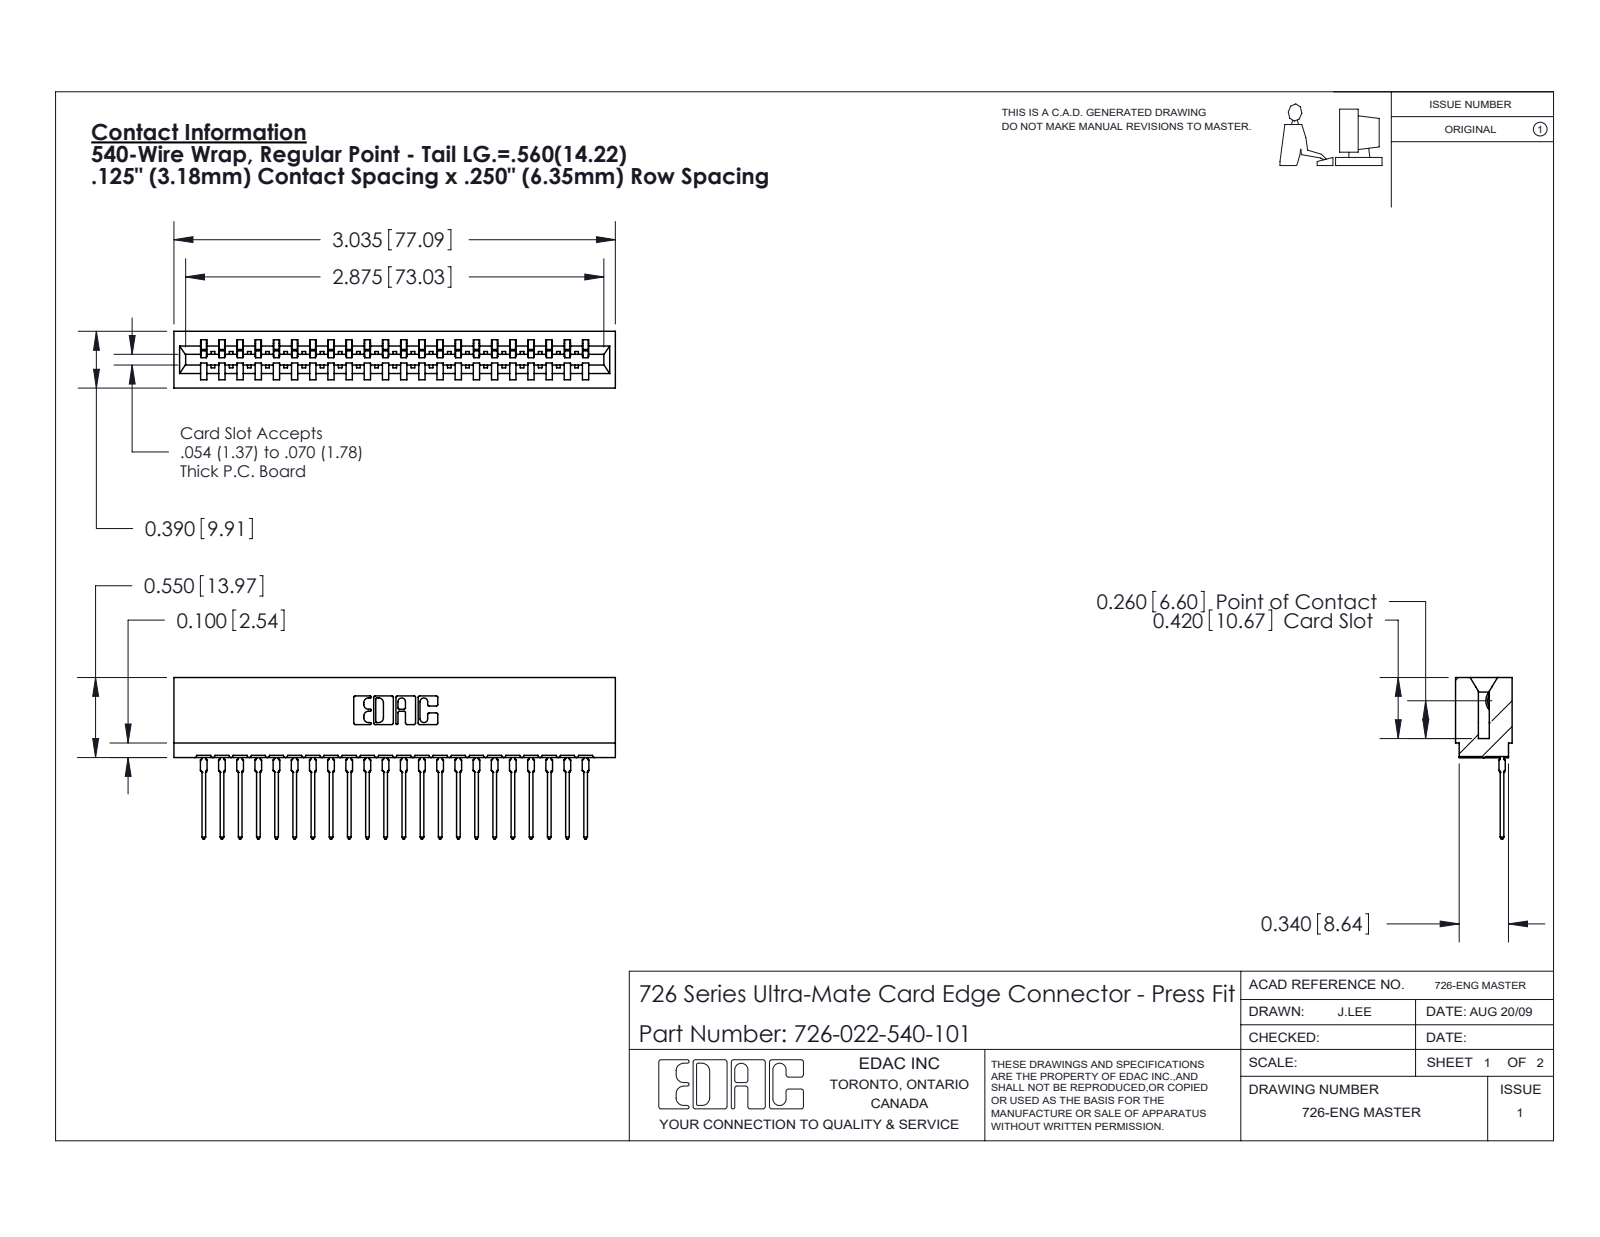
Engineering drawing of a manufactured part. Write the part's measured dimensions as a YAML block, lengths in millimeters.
part_name: "726-022-540-101; 726 Part_.515 Slot Depth - 01; 746-292-001_540"
step_written_by: "SolidWorks 2020 (CONFIG_CONTROL_DESIGN)"
units: millimeters
bodies: {solids: 23, faces: 2473, planar: 1441, cylindrical: 460, other: 572}
overall_size: [77.1, 28.2, 9.9]
volume: 7050
surface_area: 10730
partial_cylinders:
  - {radius: 0.5, count: 44}
  - {radius: 0.4, count: 23}
  - {radius: 0.3, count: 22}
  - {radius: 0.2, count: 6}
  - {radius: 0.8, count: 6}
  - {radius: 0.1, count: 4}
  - {radius: 0.3, count: 4}
  - {radius: 0.7, count: 3}
face_to_face_distances: [1.4, 8.5, 9.9, 0.6, 7.8, 6.4, 2.1, 1.1, 31.8, 3.2]
